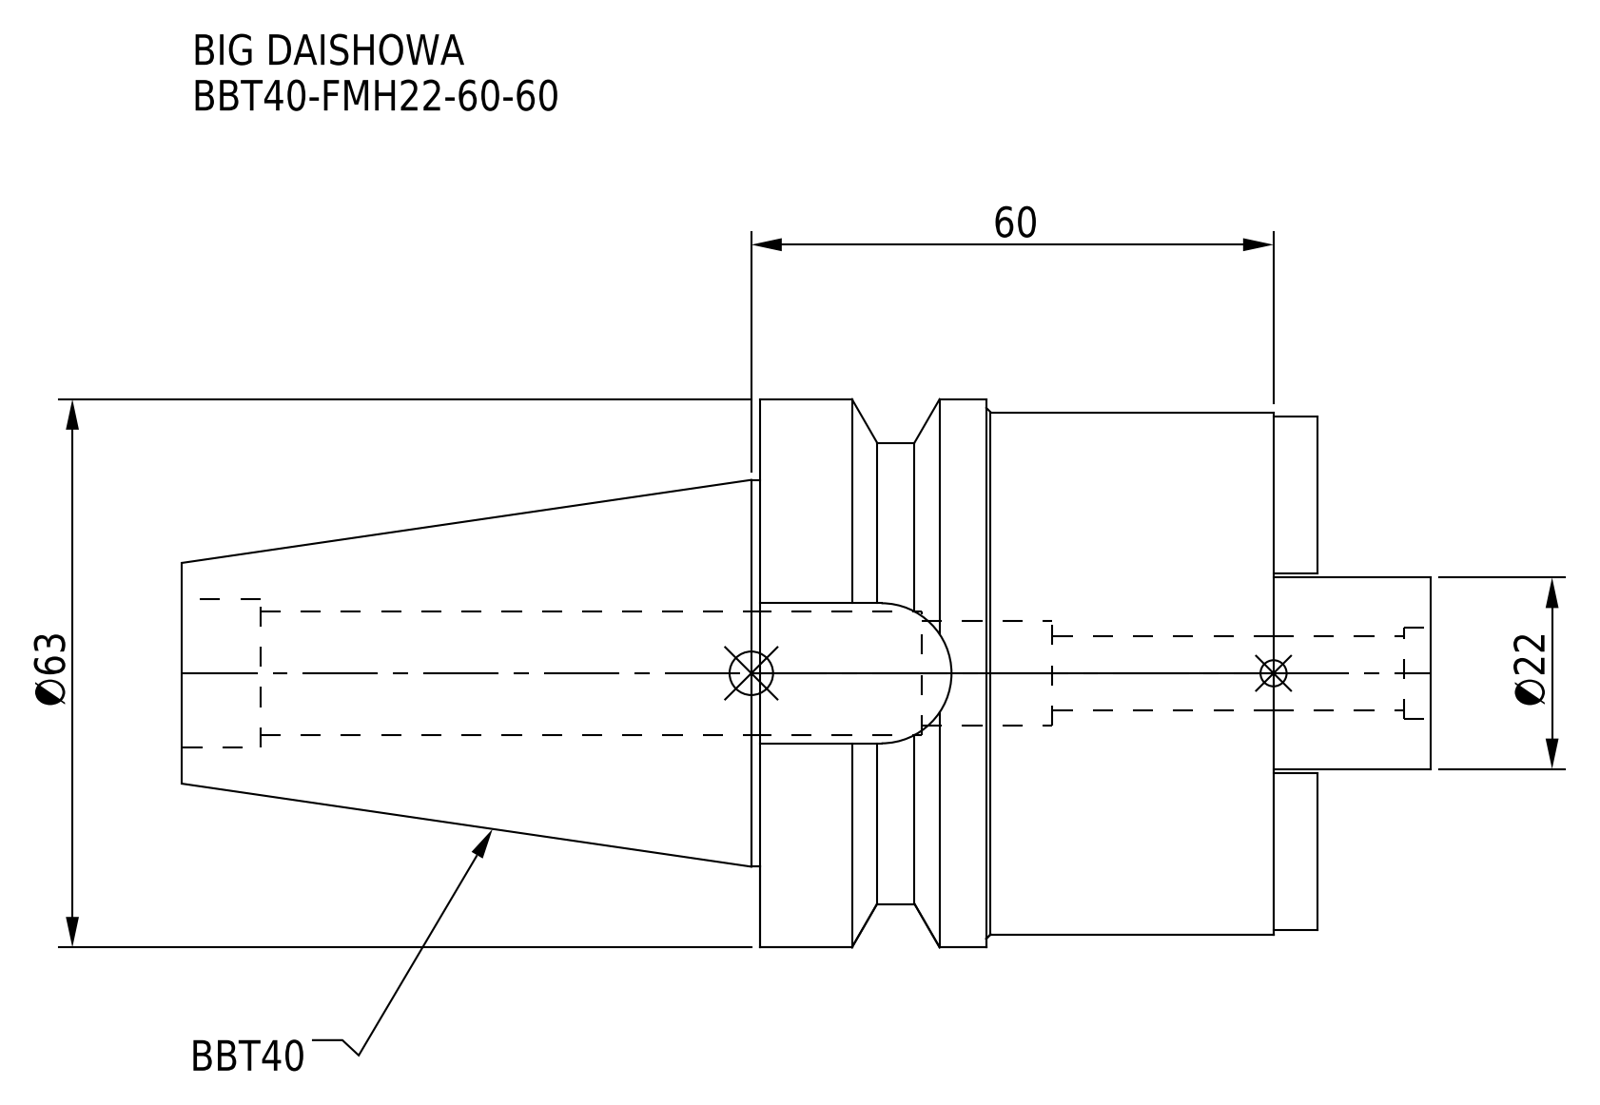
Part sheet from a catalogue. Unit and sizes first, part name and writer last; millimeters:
Units: millimetres
Overall size (bounding box): 143.4 × 63 × 63
Round holes (diameter × count): ⌀8.5 ×1, ⌀10.5 ×1, ⌀12 ×1, ⌀14.2 ×1, ⌀17 ×1
Round bosses / shafts (diameter × count): ⌀63 ×1, ⌀60 ×1, ⌀53 ×1, ⌀44.45 ×1, ⌀22 ×1
Partial cylindrical surfaces — rounded edges, fillets, slot ends (radius × count): R8.05 ×1
Main face-to-face distances: 59, 18, 5, 64, 17.5, 27.5, 45, 13, 77, 143.4
Volume: 219 223 mm³ · Surface area: 32 282 mm²
Bodies: 1 solid, 61 faces (25 planar, 28 cylindrical, 8 other)
Part name (STEP PRODUCT): BBT40-FMH22-60-60
STEP written by: CREO PARAMETRIC BY PTC INC, 2016380 (AUTOMOTIVE_DESIGN)
